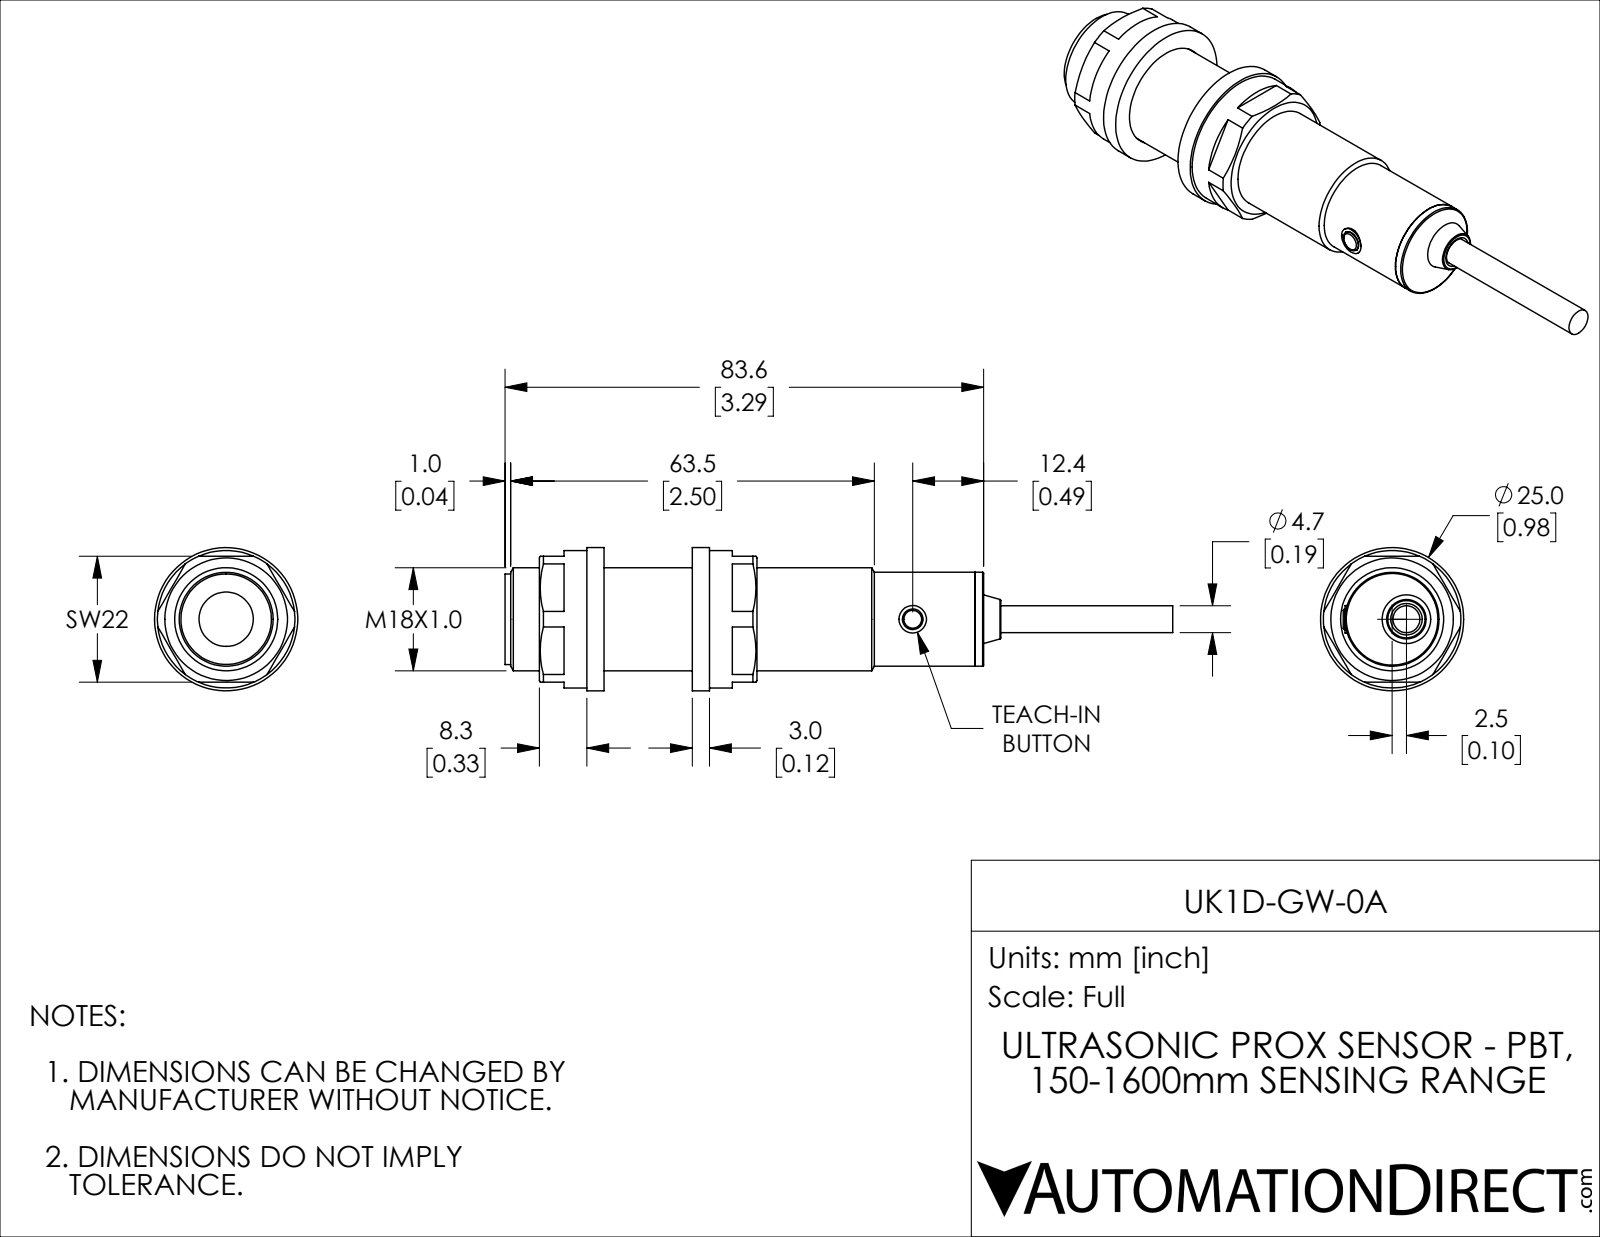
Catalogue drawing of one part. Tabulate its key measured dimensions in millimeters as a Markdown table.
| quantity | value |
| --- | --- |
| part name | UK1D-GW-0A |
| STEP written by | SolidWorks 2018 (AUTOMOTIVE_DESIGN) |
| units | millimeters |
| bodies | 10 solids, 107 faces (49 planar, 40 cylindrical, 18 other) |
| overall size | 116.6 × 25 × 25 |
| volume | 25 220 mm³ |
| surface area | 11 419 mm² |
| round holes (diameter × count) | 4.7 × 2, 3.6 × 1, 9.5 × 1, 18 × 1, 18.2 × 1 |
| round bosses / shafts (diameter × count) | 25 × 1, 24 × 1, 16.4 × 1, 15.8 × 1, 5.4 × 1, 4.8 × 1 |
| main face-to-face distances | 3, 18.4, 21.4, 67.8, 46.4, 13.3, 34.7, 81.1, 16.3, 64.8 |
| hole center spacings | 2.5 |
